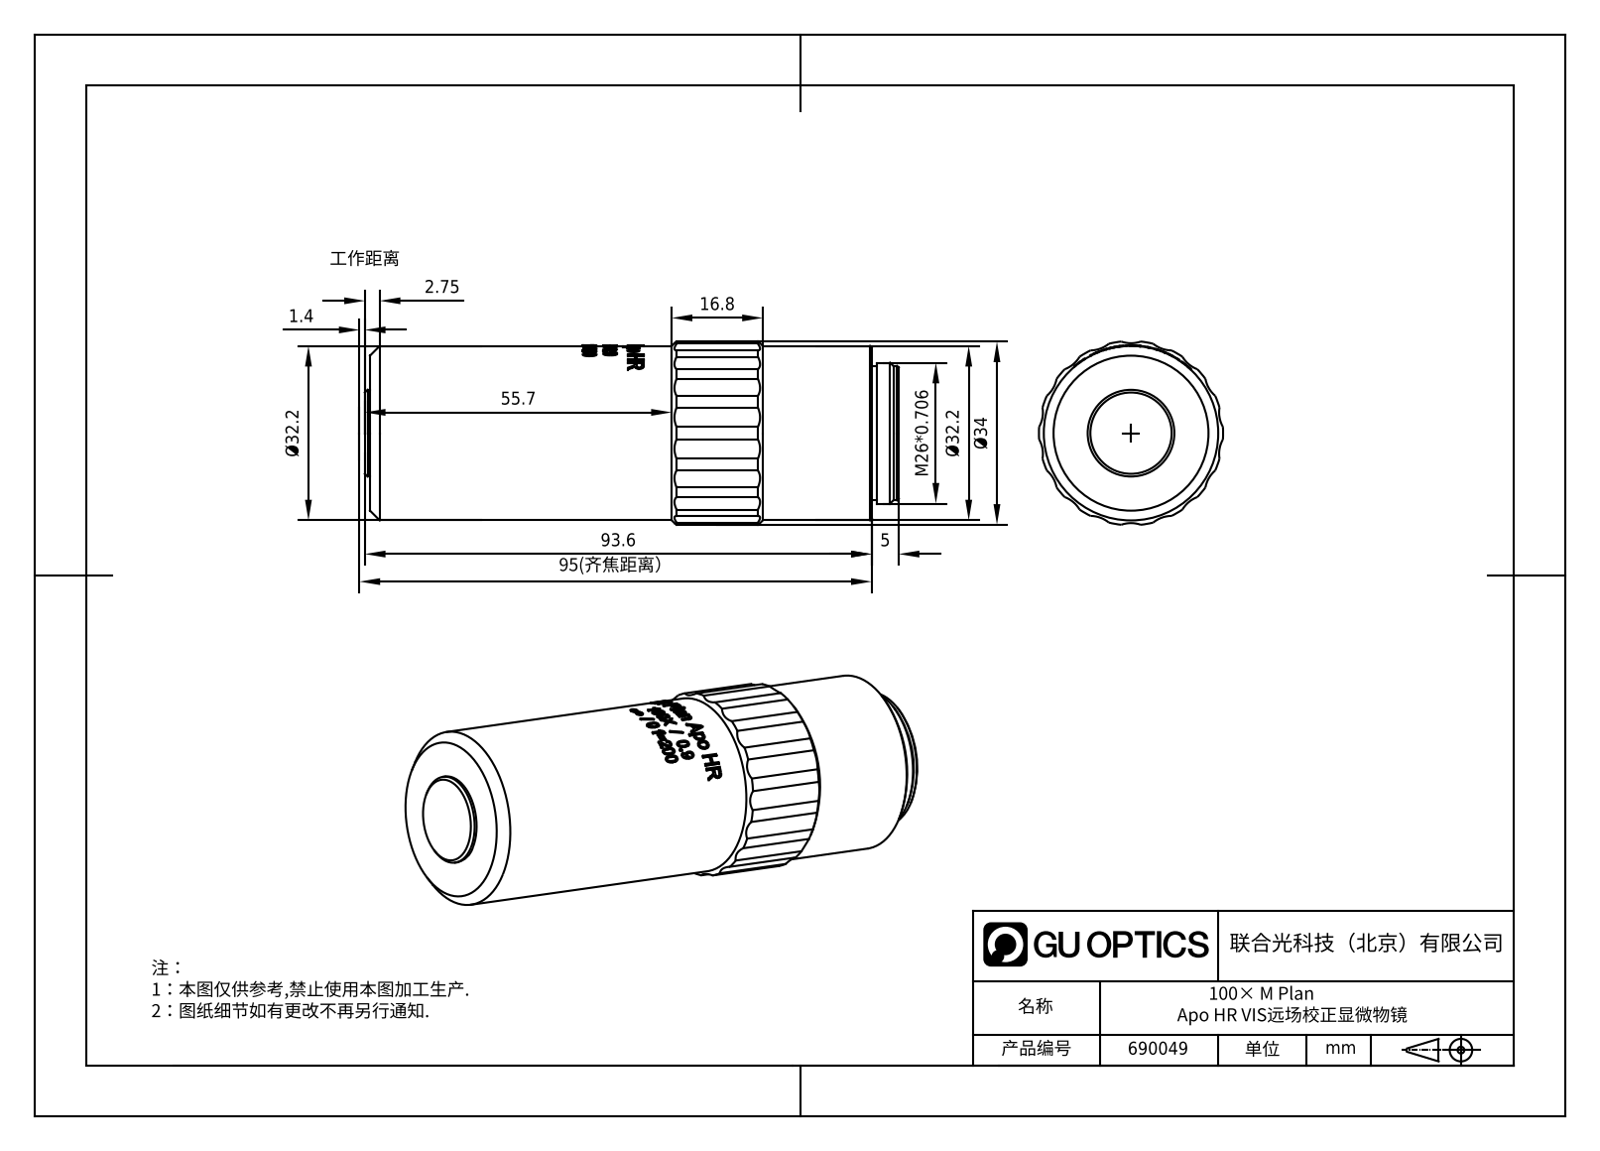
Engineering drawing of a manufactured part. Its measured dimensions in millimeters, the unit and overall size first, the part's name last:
Units: millimetres
Overall size (bounding box): 98.55 × 34 × 33.81
Round bosses / shafts (diameter × count): ⌀32.2 ×1, ⌀26 ×1, ⌀24.8 ×1, ⌀16 ×1
Partial cylindrical surfaces — rounded edges, fillets, slot ends (radius × count): R5.4 ×18, R16.2 ×1, R17 ×1
Main face-to-face distances: 97.6, 5, 92.6, 98.55, 93.55, 0.95, 4, 1, 93.6, 94.55
Volume: 79 199 mm³ · Surface area: 11 553 mm²
Bodies: 1 solid, 390 faces (114 planar, 84 cylindrical, 192 other)
Part name (STEP PRODUCT): 100X-HR НвРО-20240604
STEP written by: SolidWorks 2015 (AUTOMOTIVE_DESIGN)
